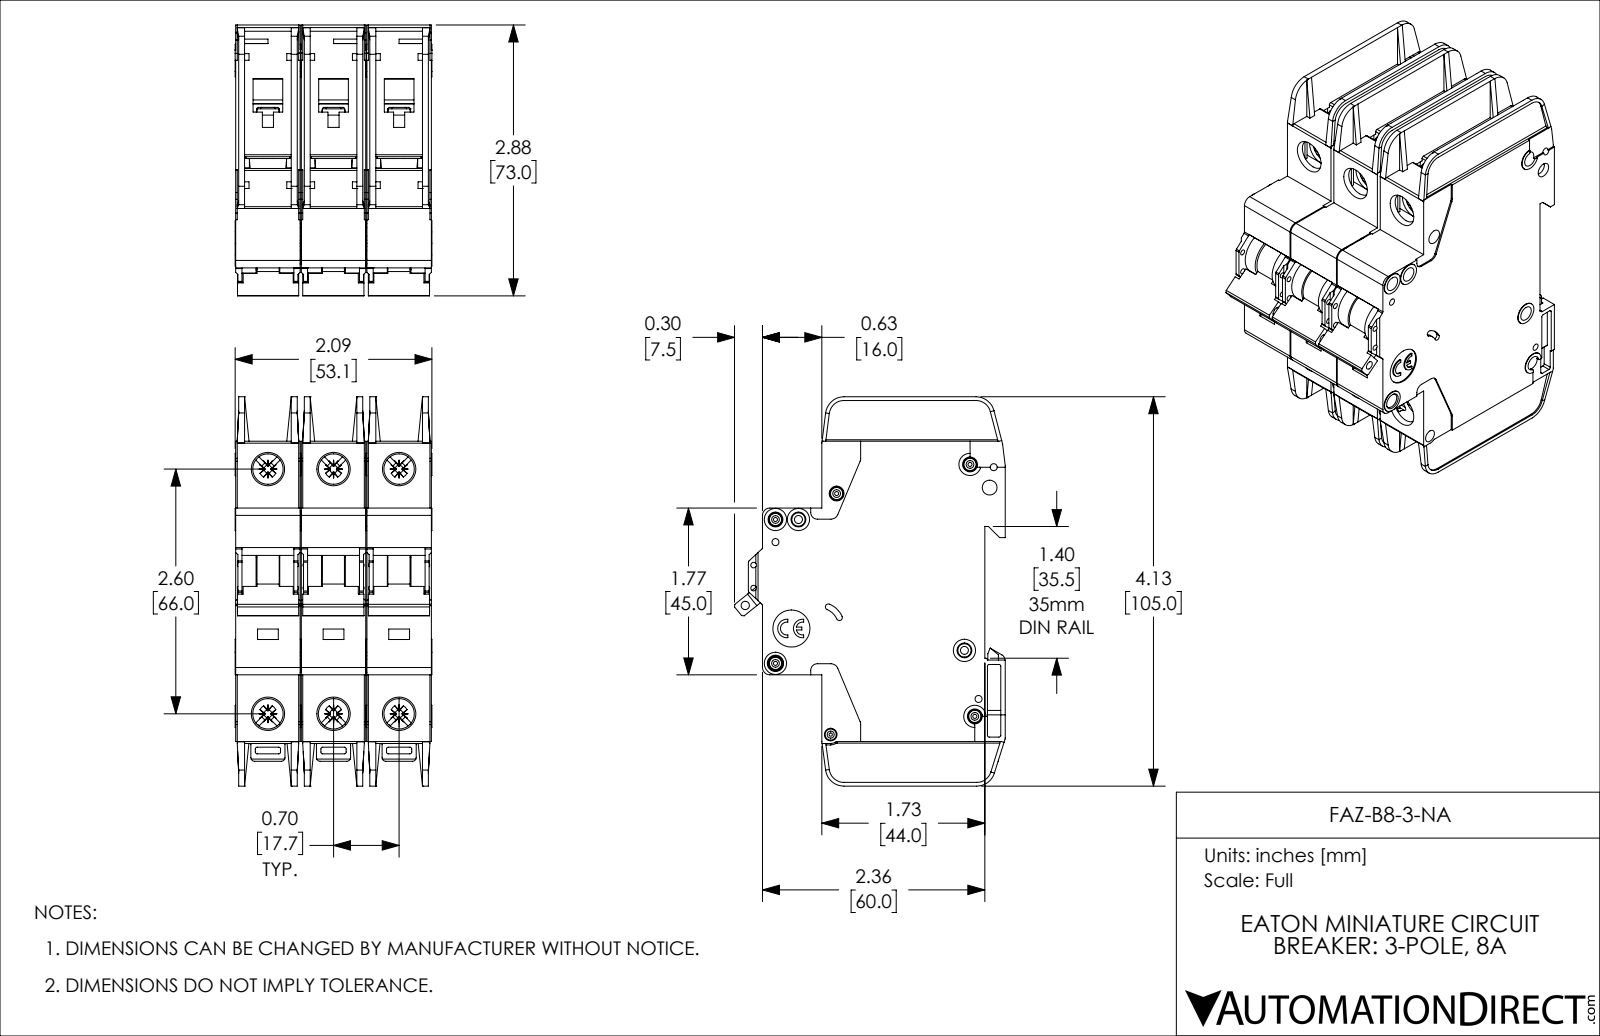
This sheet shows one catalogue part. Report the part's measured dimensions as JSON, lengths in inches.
{"part_name": "FAZ-B8-3-NA", "step_written_by": "SolidWorks 2019 (AUTOMOTIVE_DESIGN)", "units": "inches", "bodies": {"solids": 3, "faces": 3381, "planar": 2013, "cylindrical": 1071, "other": 297}, "overall_size": [4.134, 2.876, 2.091], "volume_in3": 14.05, "surface_area_in2": 123, "round_holes": [[0.157, 8], [0.323, 6], [0.043, 5], [0.075, 4], [0.059, 2], [0.085, 2], [0.035, 1], [0.089, 1], [0.098, 1], [0.134, 1], [0.394, 1]], "round_bosses_or_shafts": [[0.13, 5], [0.236, 4], [0.118, 4], [0.098, 3]], "partial_cylinders_radius": [[0.02, 72], [0.016, 30], [0.039, 18], [0.043, 12], [0.079, 12], [0.008, 6], [0.01, 6], [0.028, 6]], "face_to_face_distances": [0.697, 0.047, 1.394, 0.685, 0.591, 1.382, 0.744, 0.65, 0.106, 0.094], "hole_center_spacings": [0.697, 2.69, 2.598, 0.244, 0.537, 0.87, 1.394, 2.948]}
